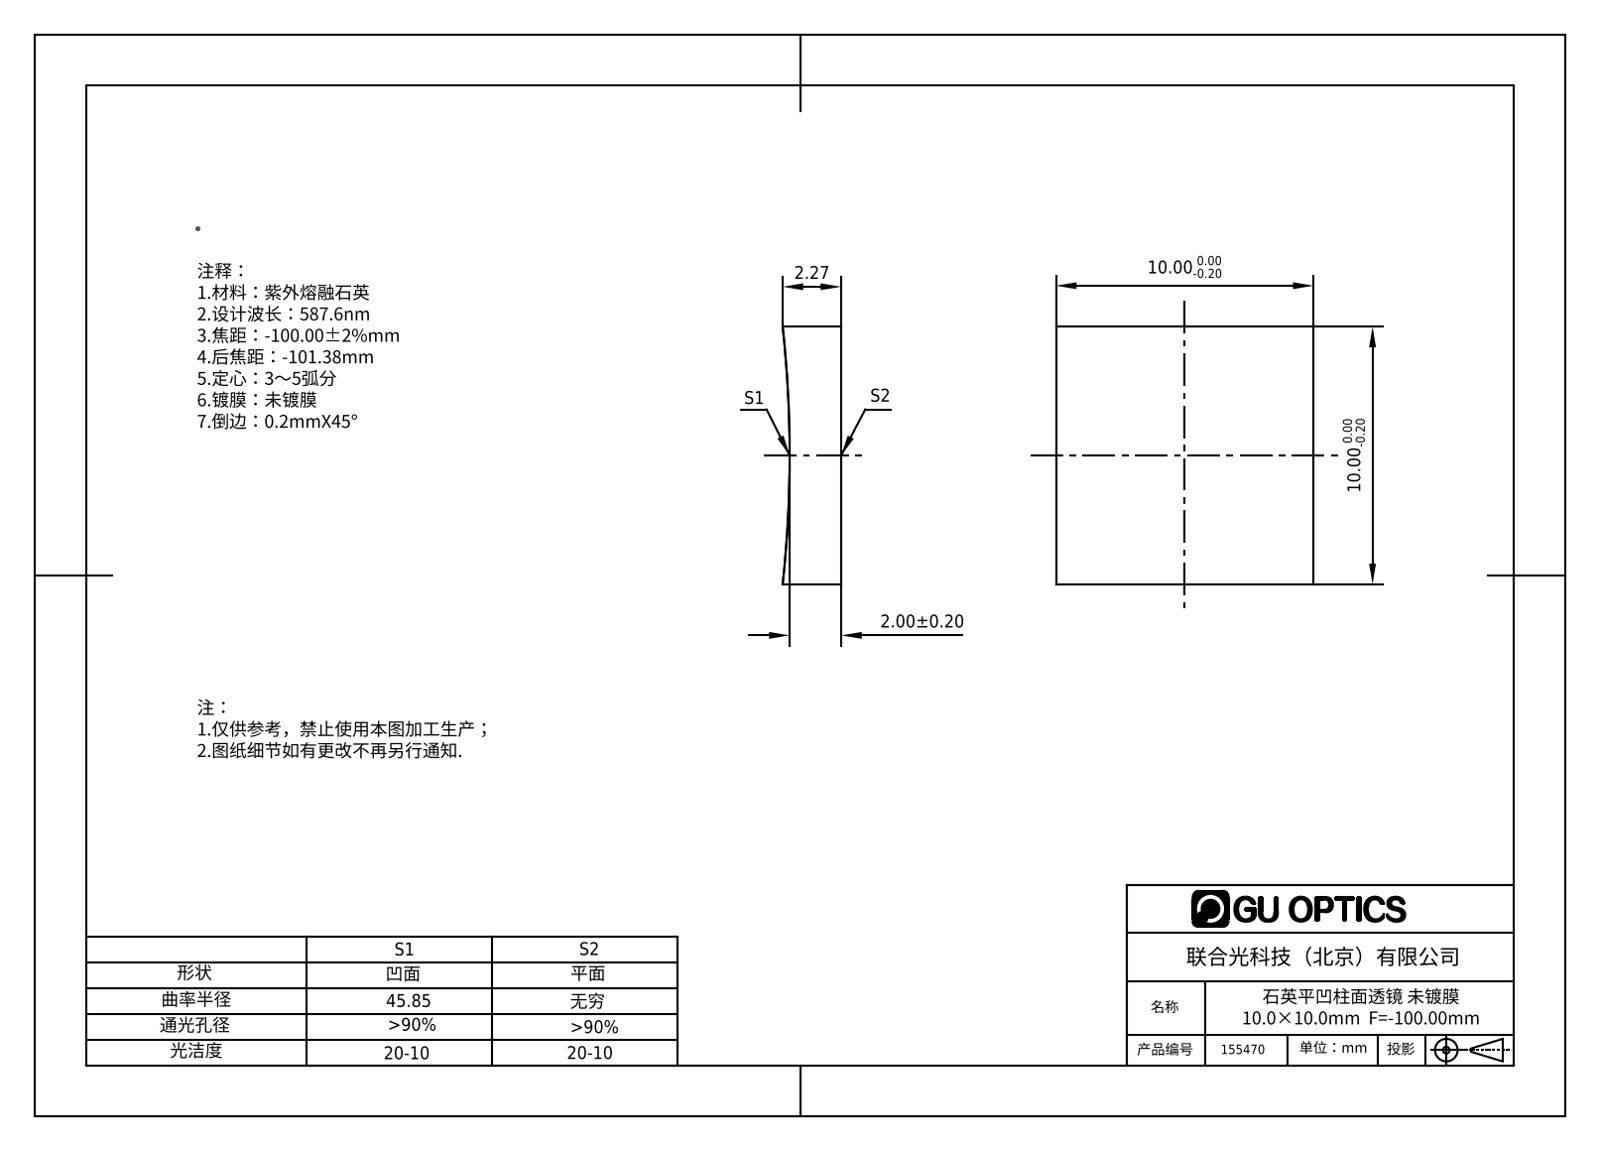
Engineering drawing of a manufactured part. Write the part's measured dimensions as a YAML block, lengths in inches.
part_name: "155470"
step_written_by: "SolidWorks 2016 (AUTOMOTIVE_DESIGN)"
units: inches
bodies: {solids: 1, faces: 6, planar: 5, cylindrical: 1, other: 0}
overall_size: [0.394, 0.394, 0.089]
volume: 0.013
surface_area: 0.445
partial_cylinders:
  - {radius: 1.805, count: 1}
face_to_face_distances: [0.394]
